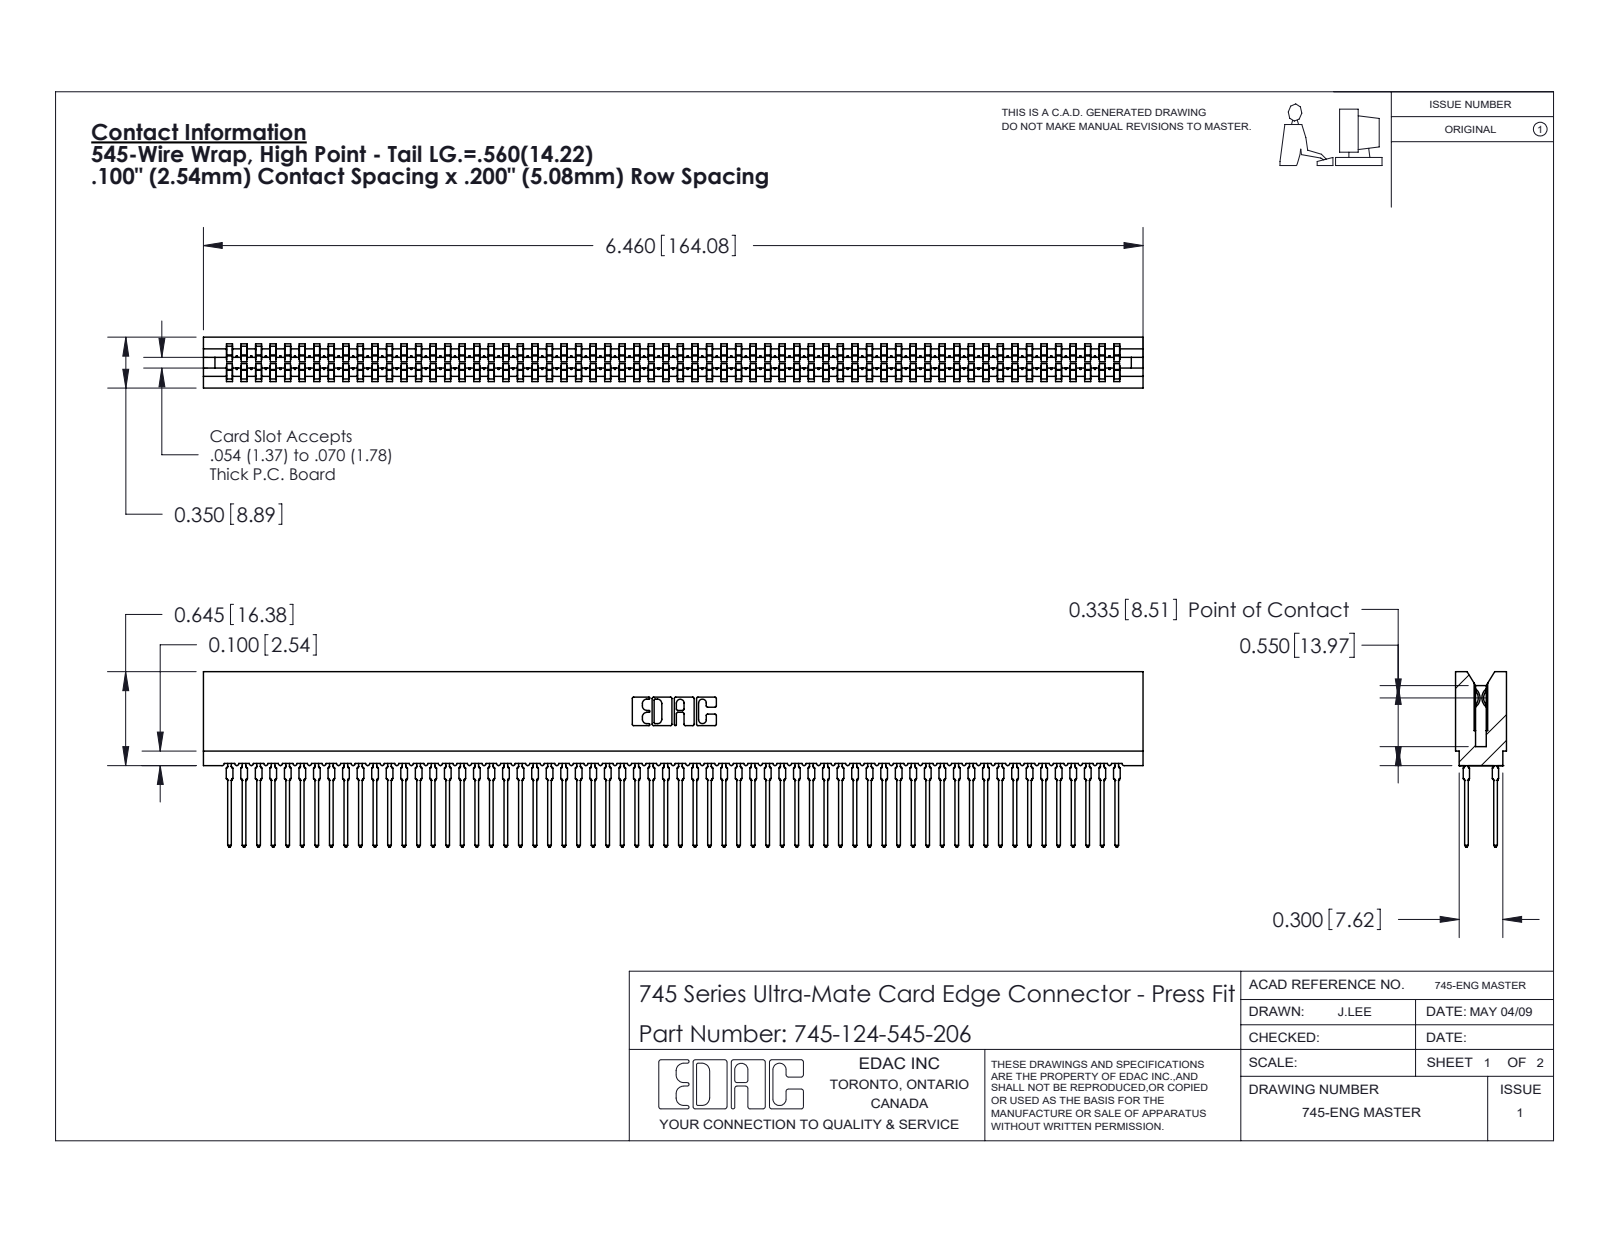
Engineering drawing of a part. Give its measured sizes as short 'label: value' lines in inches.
name: 745 Part_Insulator Option - 06; 745-124-545-206; 745-292-001_545
written by: SolidWorks 2020 (CONFIG_CONTROL_DESIGN)
unit: in
bodies: 125 solids, 11194 faces (5760 planar, 2210 cylindrical, 3224 other)
size: 6.46 × 1.206 × 0.35
volume: 0.92 in³; area: 51.17 in²
rounds: 248× R0.021, 124× R0.015, 22× R0.01, 8× R0.005, 8× R0.011, 6× R0.007, 6× R0.031, 3× R0.026
face distances: 0.063, 0.287, 0.35, 0.2, 0.045, 0.305, 0.018, 0.243, 0.138, 0.212
